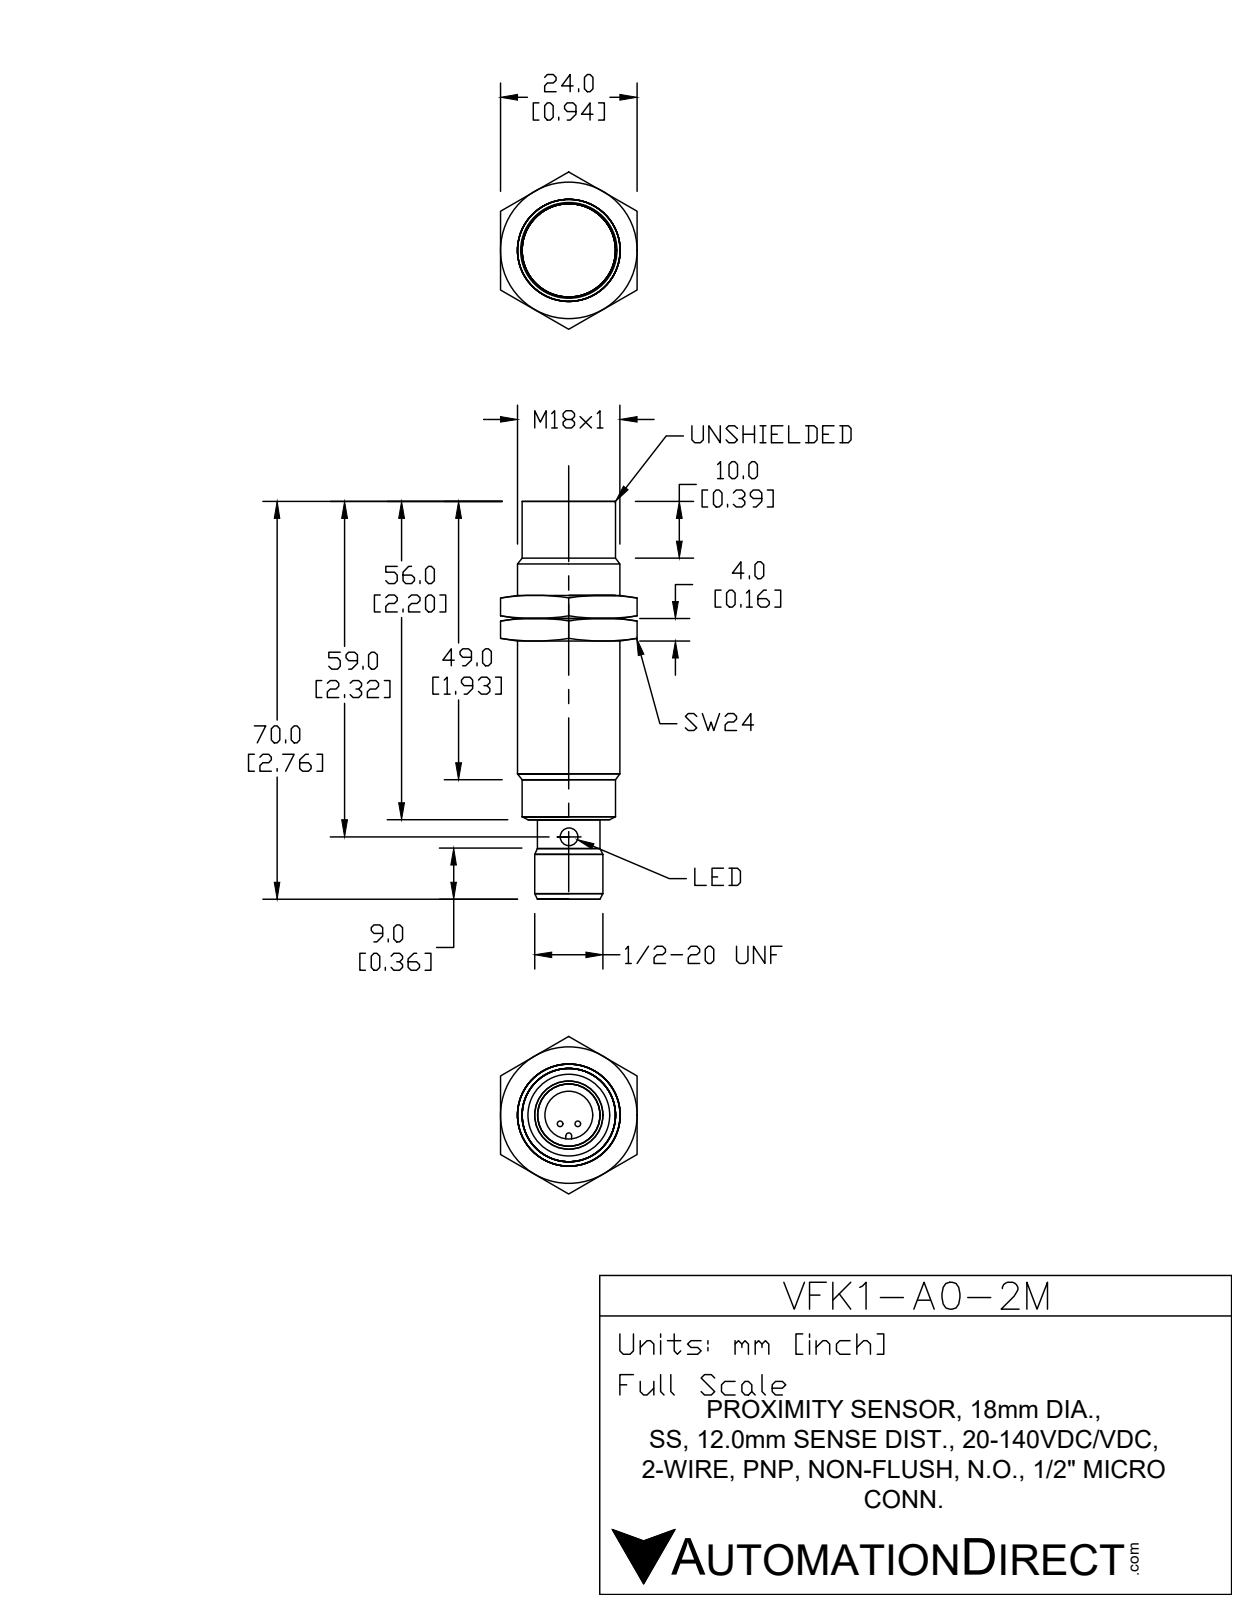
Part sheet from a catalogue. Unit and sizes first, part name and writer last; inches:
Units: inches
Overall size (bounding box): 2.756 × 1.091 × 0.945
Round holes (diameter × count): ⌀0.098 ×1, ⌀0.118 ×1, ⌀0.299 ×1, ⌀0.666 ×1
Round bosses / shafts (diameter × count): ⌀0.709 ×1, ⌀0.665 ×1, ⌀0.654 ×1, ⌀0.63 ×1, ⌀0.5 ×1, ⌀0.445 ×1, ⌀0.417 ×1
Partial cylindrical surfaces — rounded edges, fillets, slot ends (radius × count): R0.008 ×8, R0.173 ×1, R0.197 ×1
Main face-to-face distances: 0.157, 0.945, 0.315, 1.339, 1.181, 1.024, 0.906, 1.063, 1.22, 2.244
Volume: 1.029 in³ · Surface area: 9.814 in²
Bodies: 3 solids, 125 faces (27 planar, 44 cylindrical, 54 other)
Part name (STEP PRODUCT): VFK1-A0-2M
STEP written by: SolidWorks 2017 (AUTOMOTIVE_DESIGN)
